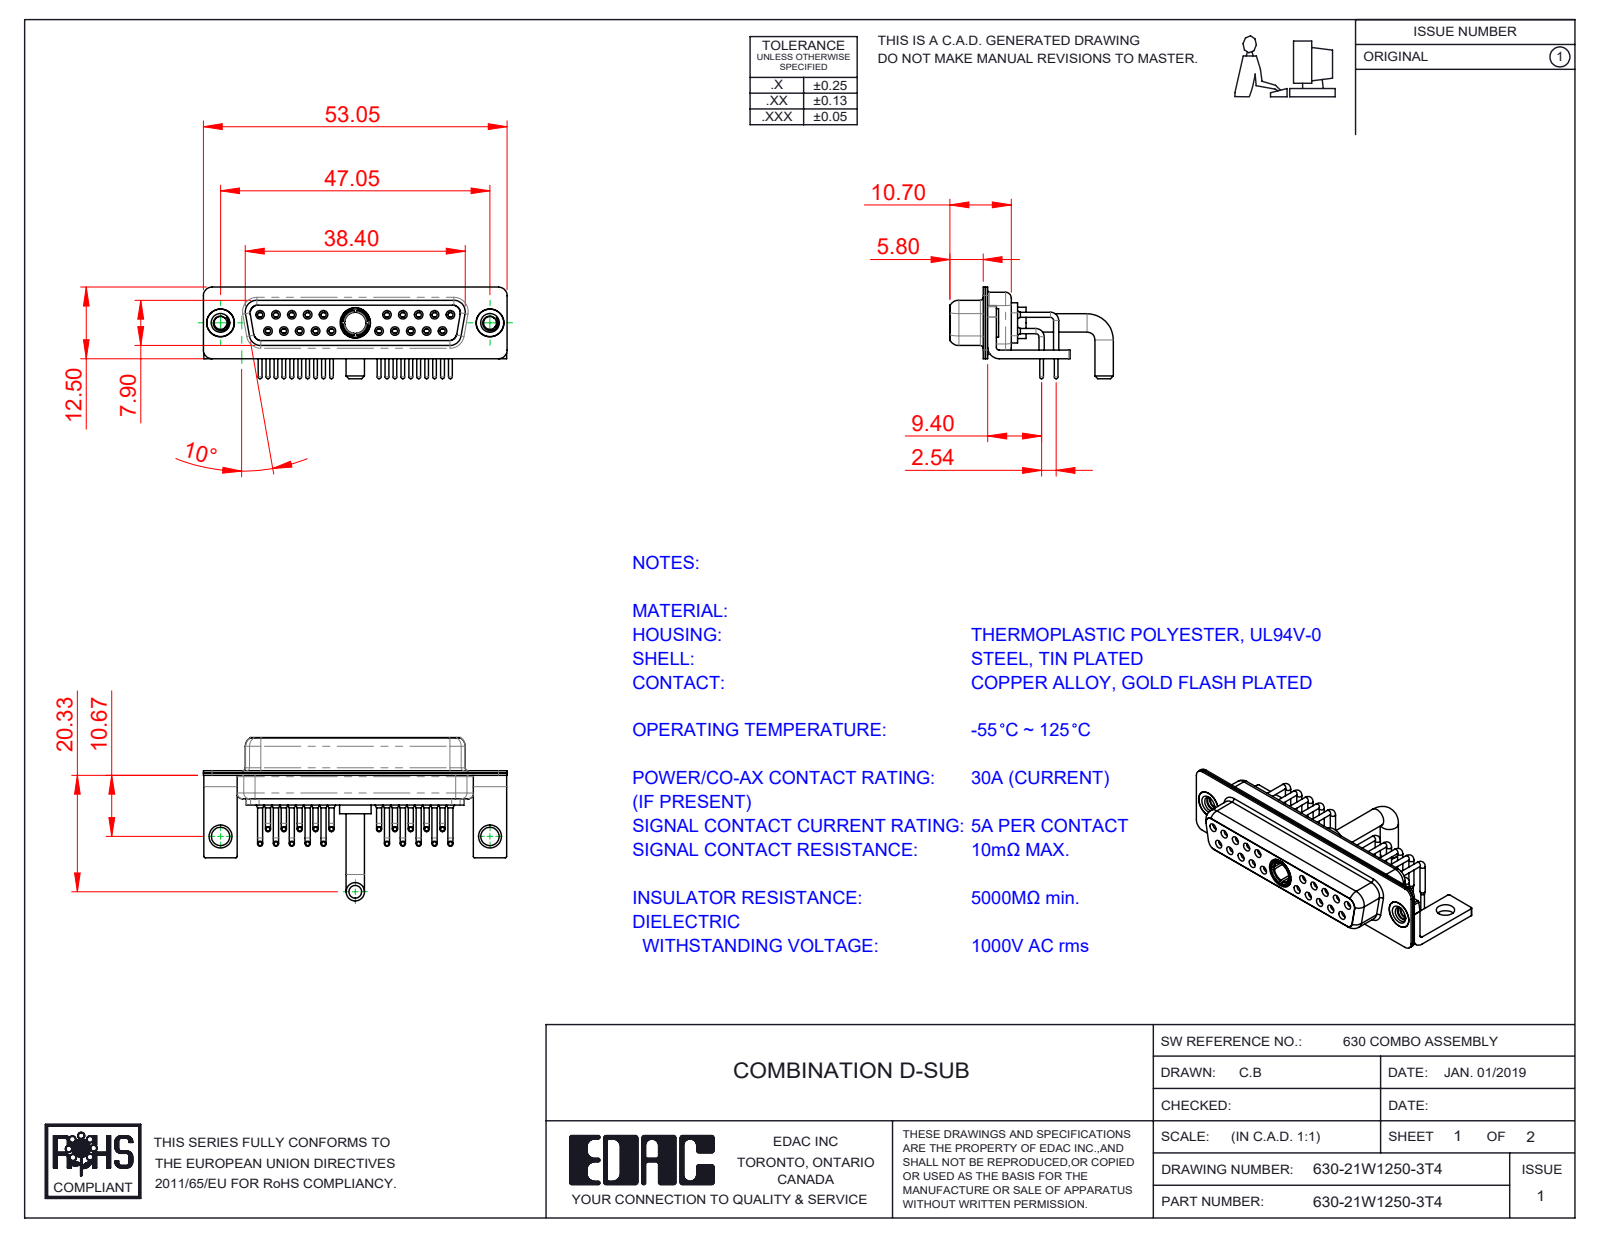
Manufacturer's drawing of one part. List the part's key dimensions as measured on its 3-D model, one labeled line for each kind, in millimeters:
Part name (STEP PRODUCT): 630Combo Threaded Rivet_3; 630Combo Shell Front_25 Contacts; 630Combo Stabilizer Bracket; 630Combo Contact Row 2 (+5 more)
STEP written by: SolidWorks 2020 (CONFIG_CONTROL_DESIGN)
Units: millimetres
Bodies: 29 solids, 1457 faces (416 planar, 640 cylindrical, 401 other)
Overall size (bounding box): 53.05 × 28.53 × 16
Volume: 4 379 mm³ · Surface area: 10 027 mm²
Round holes (diameter × count): ⌀0.9 ×20, ⌀1.1 ×20, ⌀1.5 ×20, ⌀2 ×20, ⌀1.6 ×10, ⌀1.7 ×10, ⌀4.85 ×3, ⌀2.26 ×2, ⌀3.2 ×2, ⌀4 ×2, ⌀4.05 ×2, ⌀3.7 ×1
Round bosses / shafts (diameter × count): ⌀0.9 ×20, ⌀0.65 ×20, ⌀1.6 ×10, ⌀5 ×2, ⌀4.95 ×2, ⌀4.8 ×2, ⌀3.2 ×2, ⌀5.5 ×1
Partial cylindrical surfaces — rounded edges, fillets, slot ends (radius × count): R0.25 ×16, R1.5 ×16, R2 ×13, R1.35 ×8, R1.6 ×8, R0.5 ×5, R0.6 ×4, R0.65 ×4
Main face-to-face distances: 0.4, 0.45, 1.4, 8.45, 1.8, 0.8, 8.9, 6.2, 7.05, 1.5
Hole centre spacings: 3.16, 2.77, 5.54, 8.31, 5.04, 19.39, 20.97, 22.16
